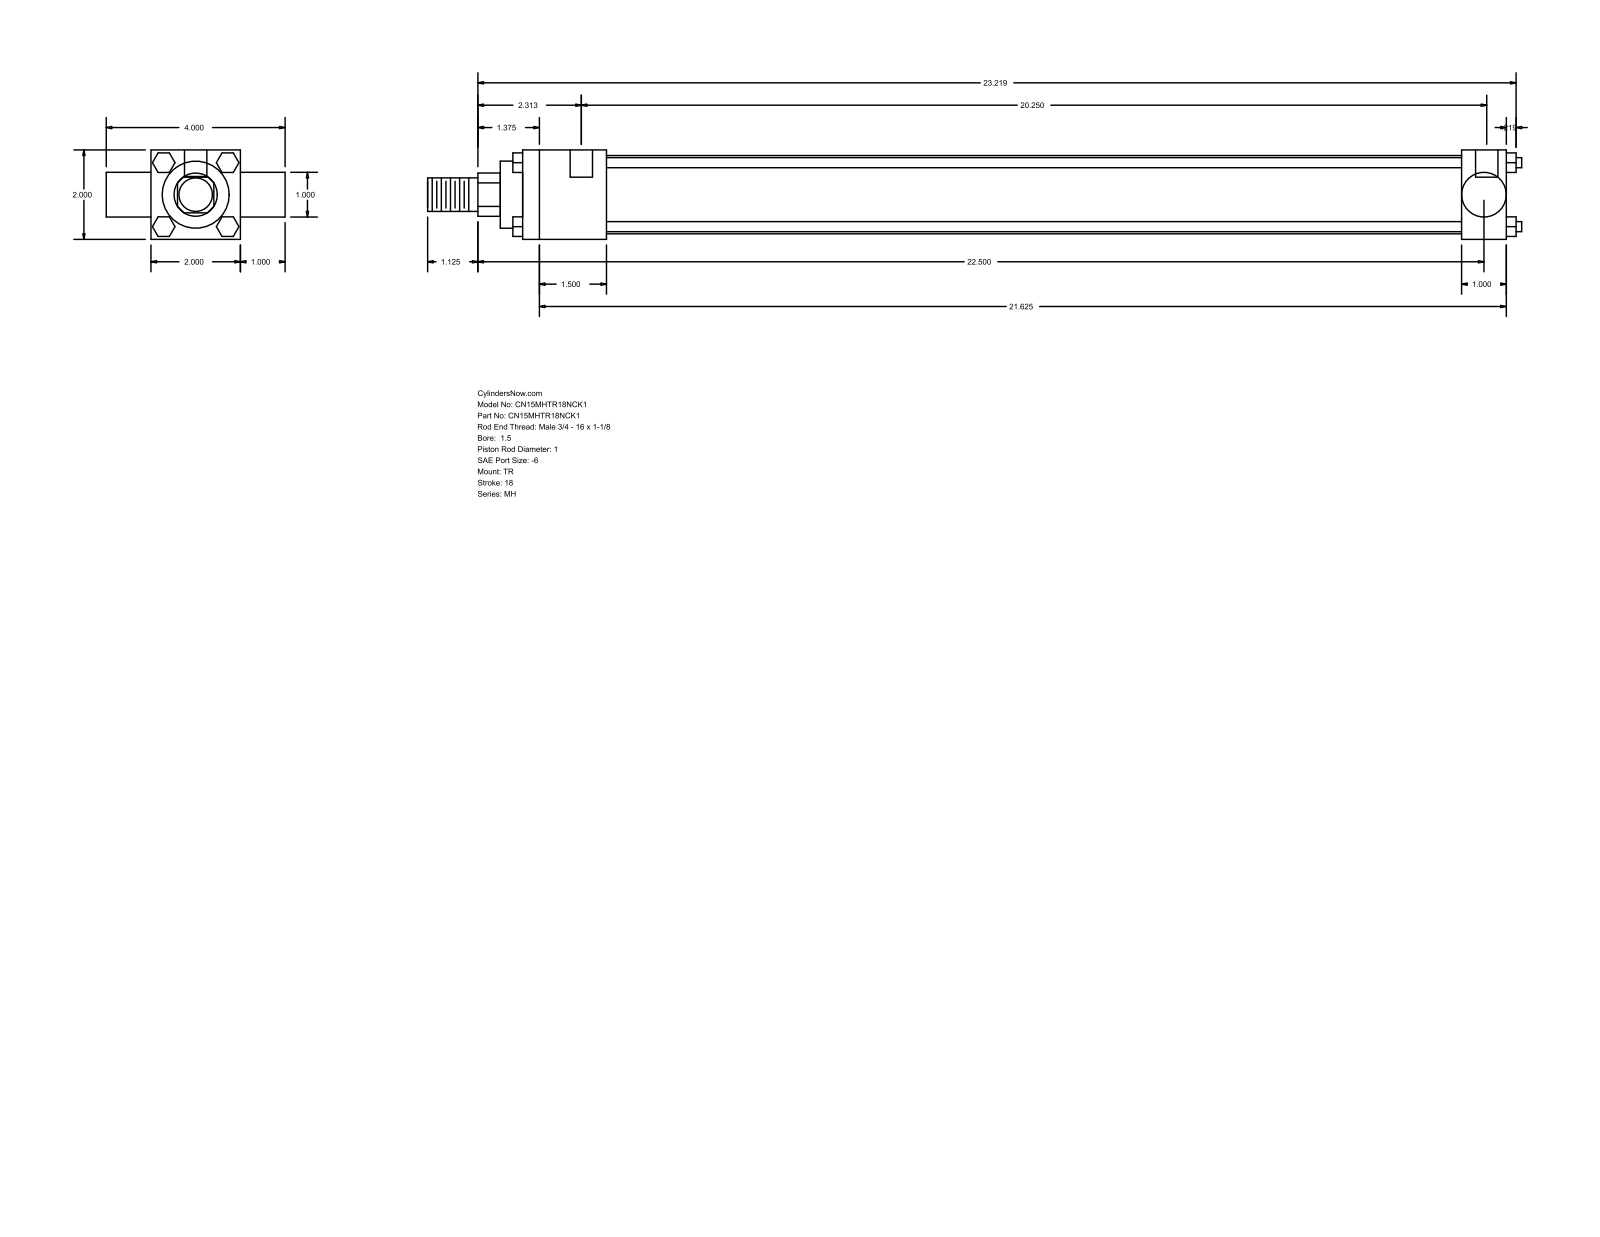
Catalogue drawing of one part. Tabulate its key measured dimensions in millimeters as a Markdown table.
| quantity | value |
| --- | --- |
| part name | MH_TR__0150_1 |
| STEP written by | GSSL Pune (CONFIG_CONTROL_DESIGN) |
| units | millimeters |
| bodies | 0 solids, 120 faces (92 planar, 28 cylindrical, 0 other) |
| overall size | 621.51 × 101.6 × 50.8 |
| round holes (diameter × count) | 5.56 × 3, 12.7 × 2 |
| round bosses / shafts (diameter × count) | 5.71 × 4, 44.45 × 1, 38.1 × 1, 25.4 × 1, 25.35 × 1, 19.05 × 1 |
| partial cylindrical surfaces (radius × count) | 12.29 × 1 |
| main face-to-face distances | 50.8, 25.4, 558.8, 76.2, 47.63, 511.17, 533.4, 485.77, 101.6, 12.7 |
| hole center spacings | 3.18, 514.35, 517.53 |
